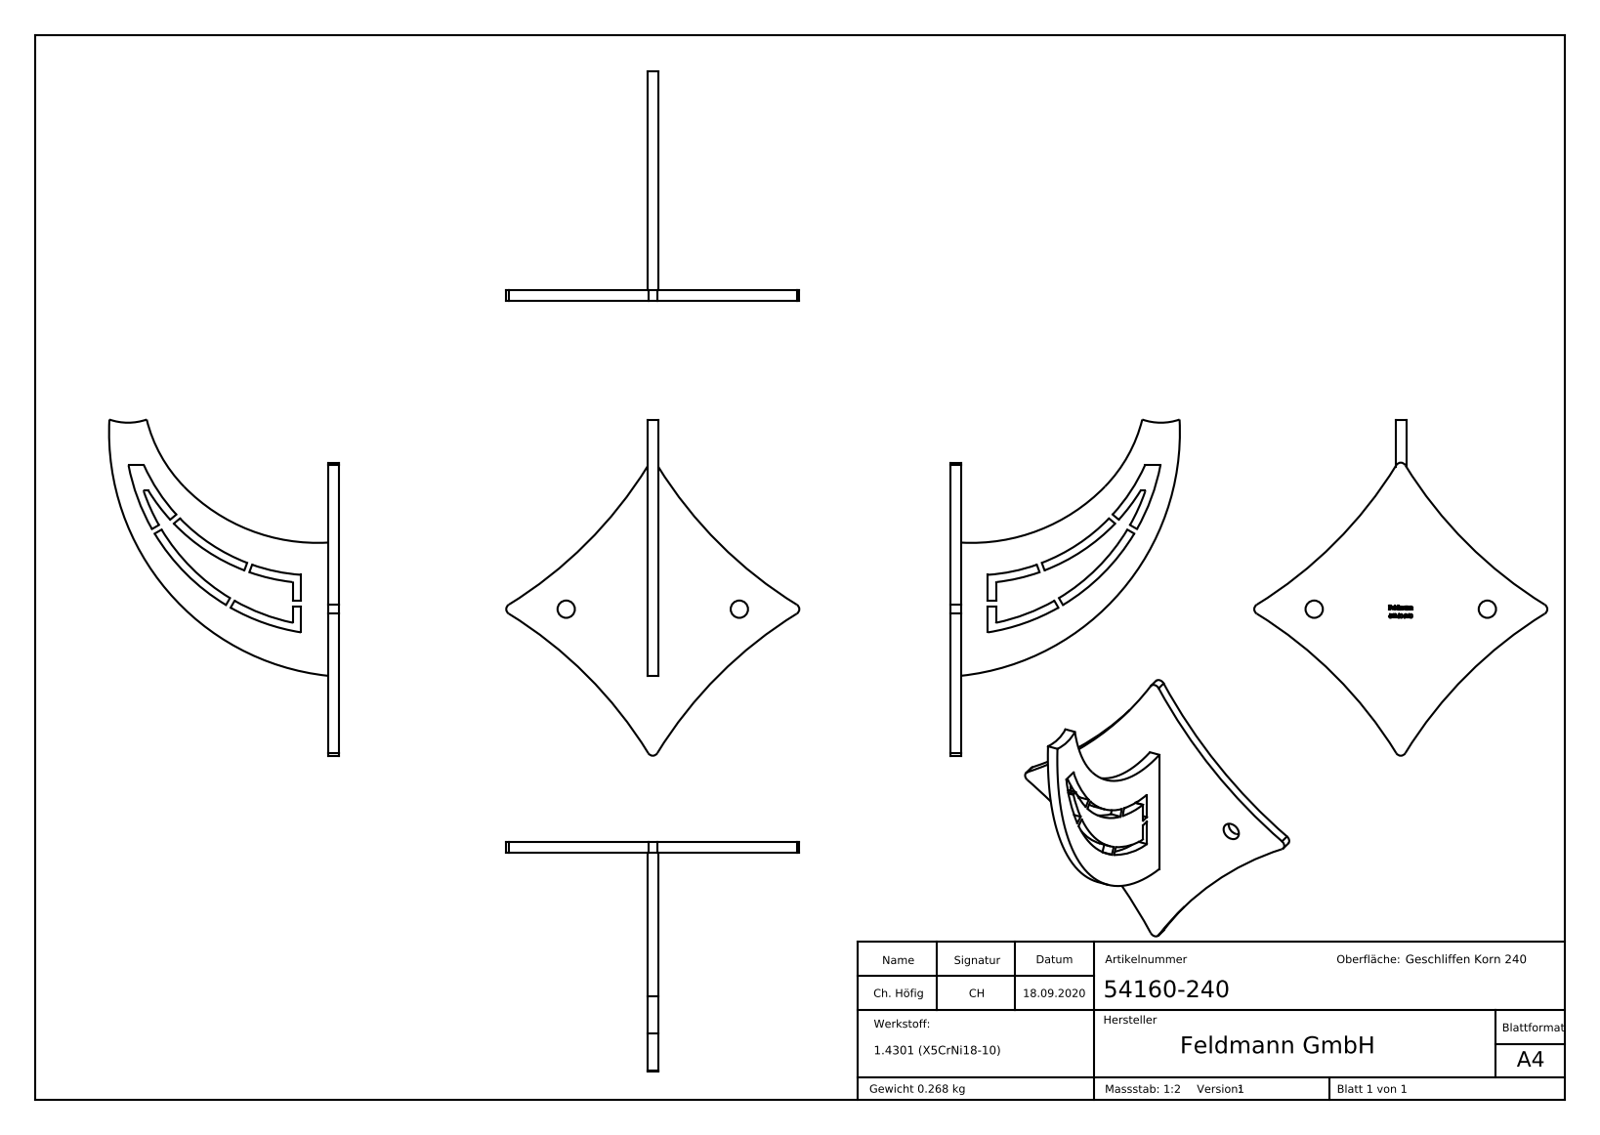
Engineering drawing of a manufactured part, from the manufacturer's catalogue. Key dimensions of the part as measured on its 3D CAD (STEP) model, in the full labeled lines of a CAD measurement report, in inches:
Part name (STEP PRODUCT): 54160-240
STEP written by: SolidWorks 2018 (CONFIG_CONTROL_DESIGN)
Units: inches
Bodies: 1 solid, 272 faces (150 planar, 33 cylindrical, 89 other)
Overall size (bounding box): 4.968 × 4.331 × 3.391
Volume: 2.071 in³ · Surface area: 32.01 in²
Round holes (diameter × count): ⌀0.256 ×2
Partial cylindrical surfaces — rounded edges, fillets, slot ends (radius × count): R0.01 ×4, R0.079 ×4, R6.299 ×4, R2.756 ×2, R0.835 ×1, R2.165 ×1, R2.874 ×1, R2.972 ×1
Main face-to-face distances: 0.157, 0.555, 0.398, 0.079, 0.673, 0.516, 0.118, 2.083, 2.004, 0.154
Hole centre spacings: 2.559
